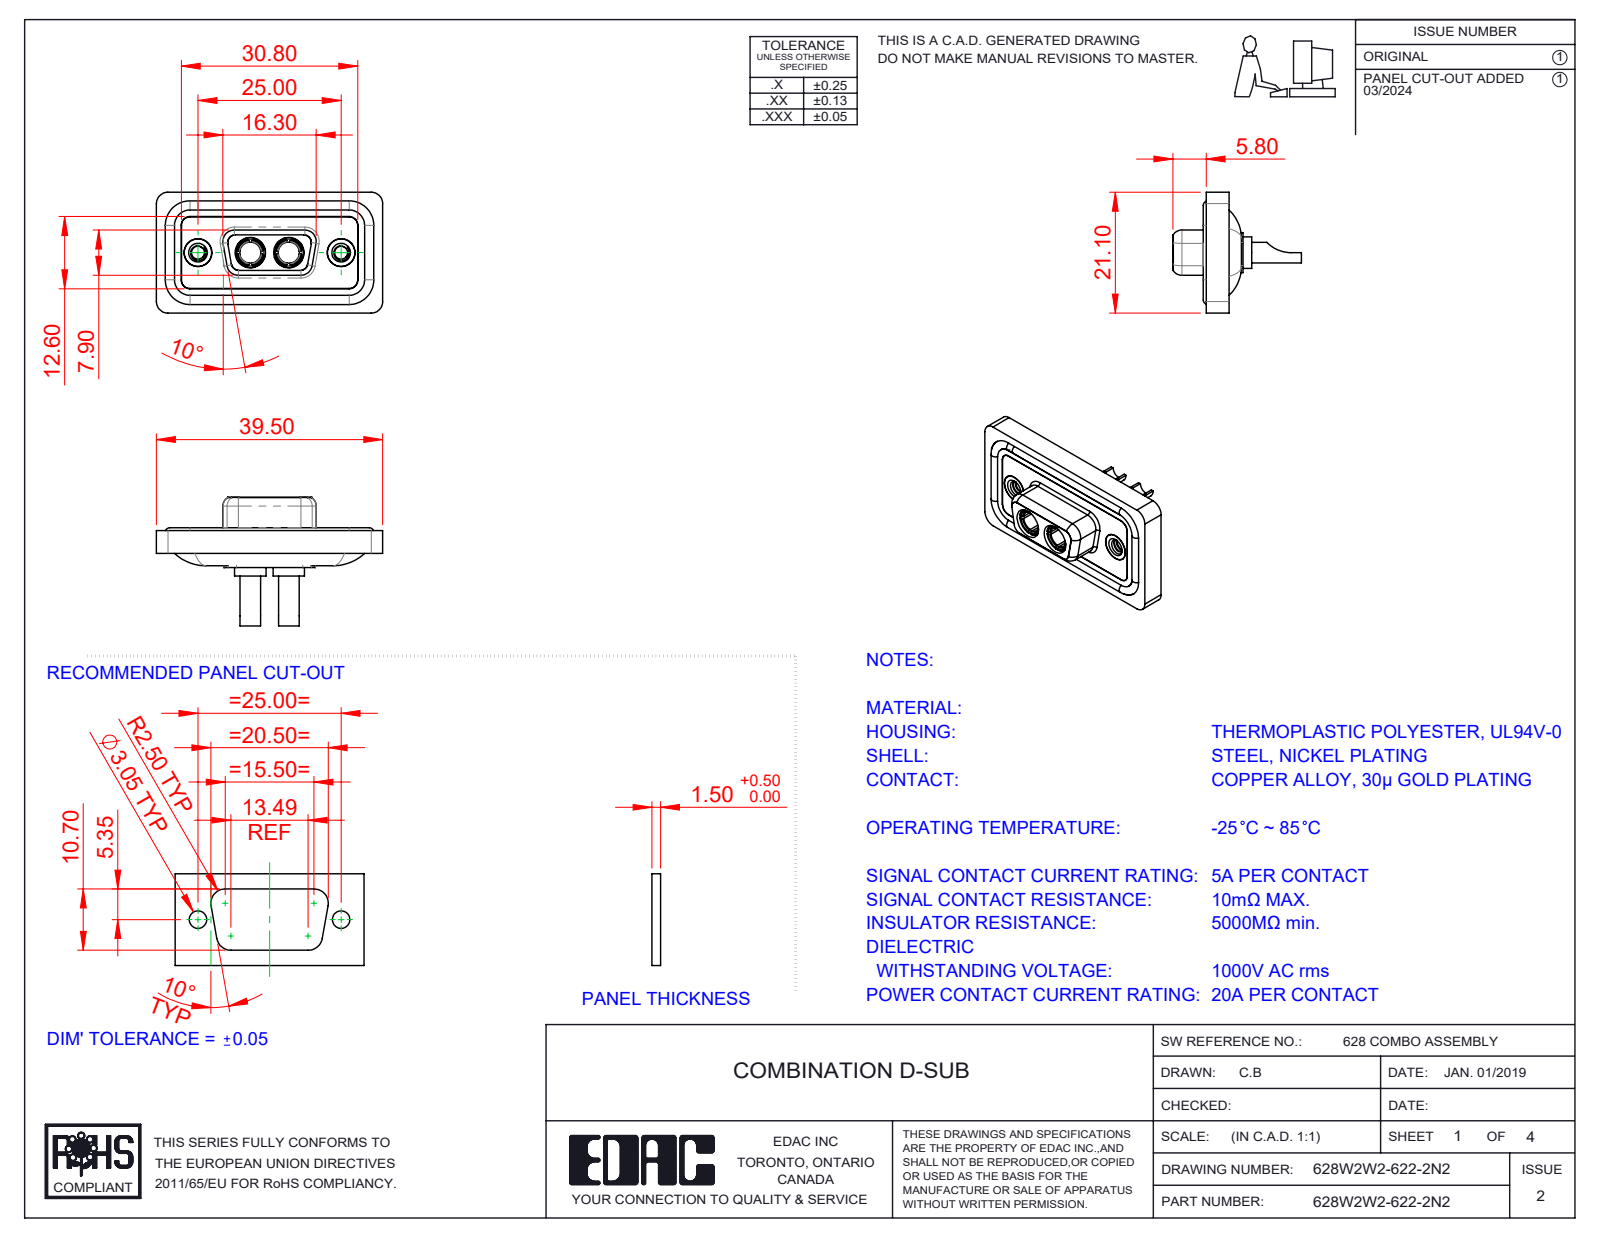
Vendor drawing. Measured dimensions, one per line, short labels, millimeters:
name: 628Combo Shell Front_09 Contacts; 628Combo Shell Rear_09 Contacts; 628W2W2-622-2N2; Power Socket_20A SC (+3 more)
written by: SolidWorks 2023 (CONFIG_CONTROL_DESIGN)
unit: mm
bodies: 11 solids, 546 faces (169 planar, 240 cylindrical, 137 other)
size: 39.5 × 22.45 × 21.1
volume: 4 738 mm³; area: 7 801 mm²
holes: 4× ⌀4.85, 2× ⌀2.26, 2× ⌀2.7, 2× ⌀3.7, 2× ⌀4, 2× ⌀4.05, 2× ⌀5, 2× ⌀5.3
bosses: 4× ⌀1.6, 2× ⌀5.5, 2× ⌀5.2, 2× ⌀4.96, 2× ⌀4.95, 2× ⌀4.8, 2× ⌀4.75, 2× ⌀3.75
rounds: 22× R1.5, 18× R2, 8× R1.35, 8× R1.6, 4× R0.25, 4× R0.5, 4× R0.6, 4× R0.65
face distances: 0.4, 1.8, 1.1, 2.9, 0.5, 1.6, 5.65, 7.45, 5.35, 1.5
hole spacings: 9.14, 15.86, 6.72, 25
